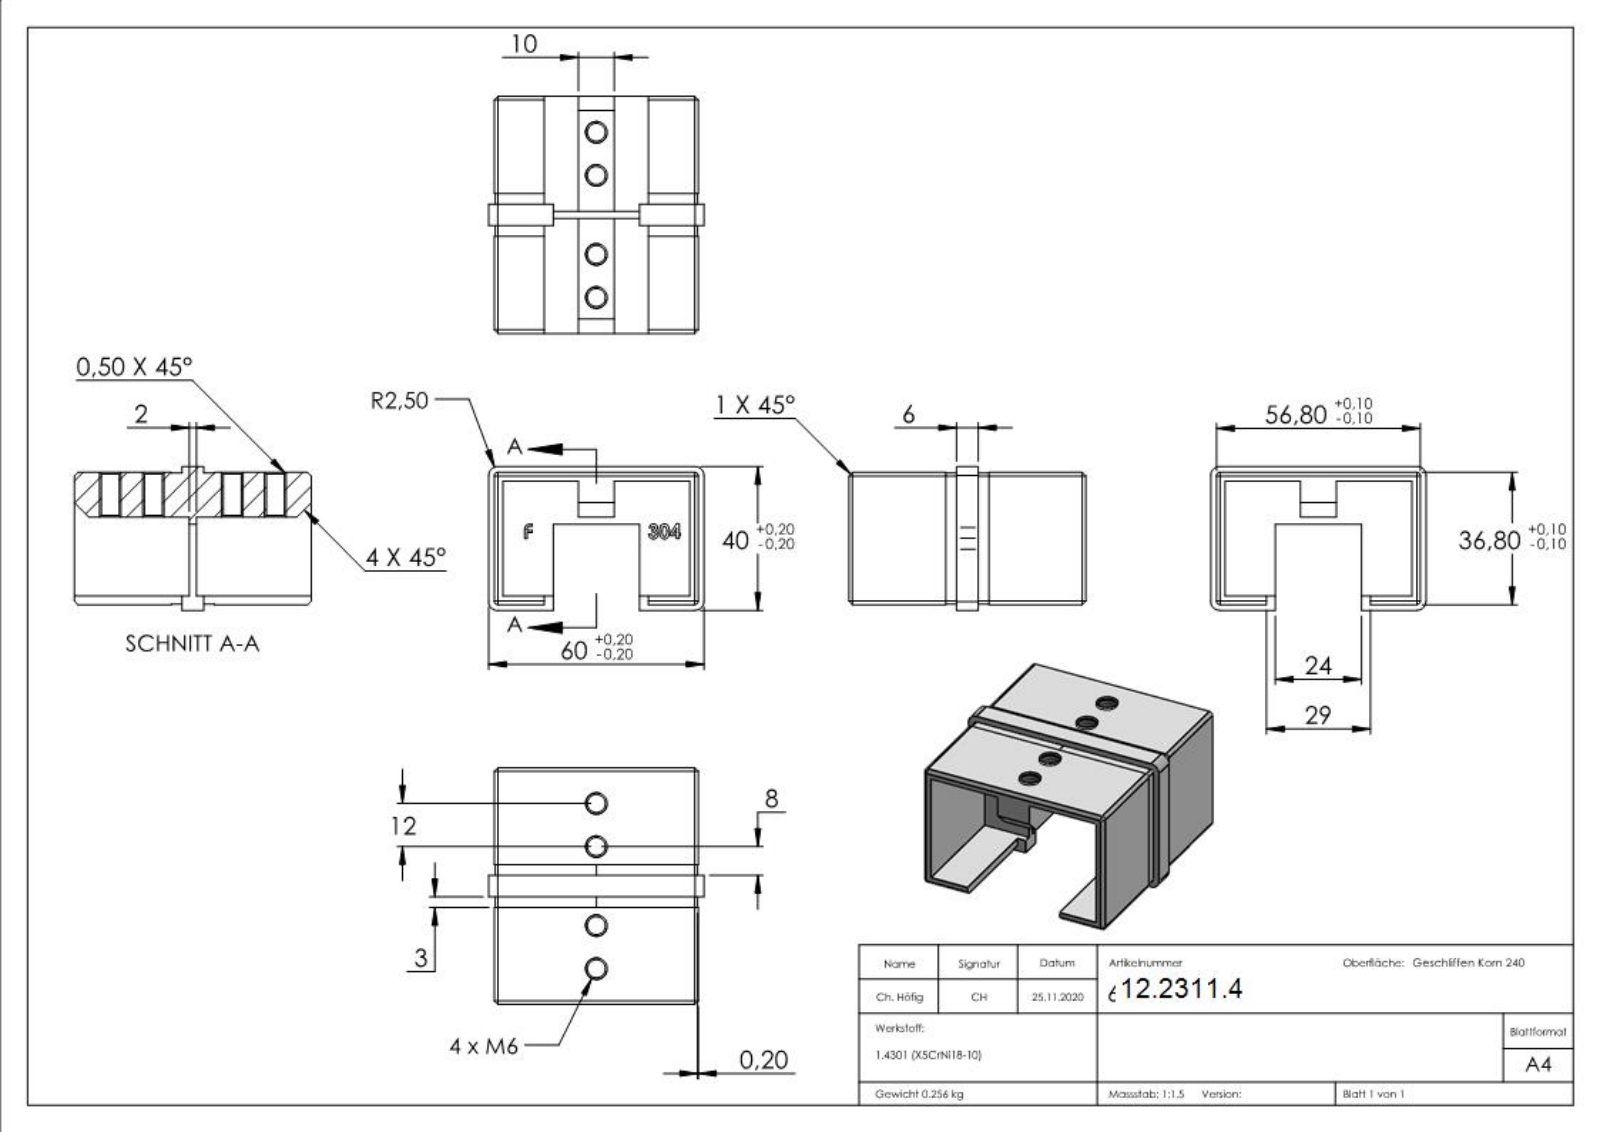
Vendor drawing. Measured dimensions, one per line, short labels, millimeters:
name: 60339-240
written by: SolidWorks 2018 (CONFIG_CONTROL_DESIGN)
unit: mm
bodies: 1 solid, 432 faces (237 planar, 28 cylindrical, 167 other)
size: 66 × 60 × 40
volume: 32 428 mm³; area: 25 169 mm²
holes: 4× ⌀5
rounds: 4× R0.8, 4× R1, 4× R2.5
face distances: 2.4, 54.4, 34.4, 52, 32, 56.8, 2, 4, 36.8, 23.4
hole spacings: 12, 34, 22, 46
